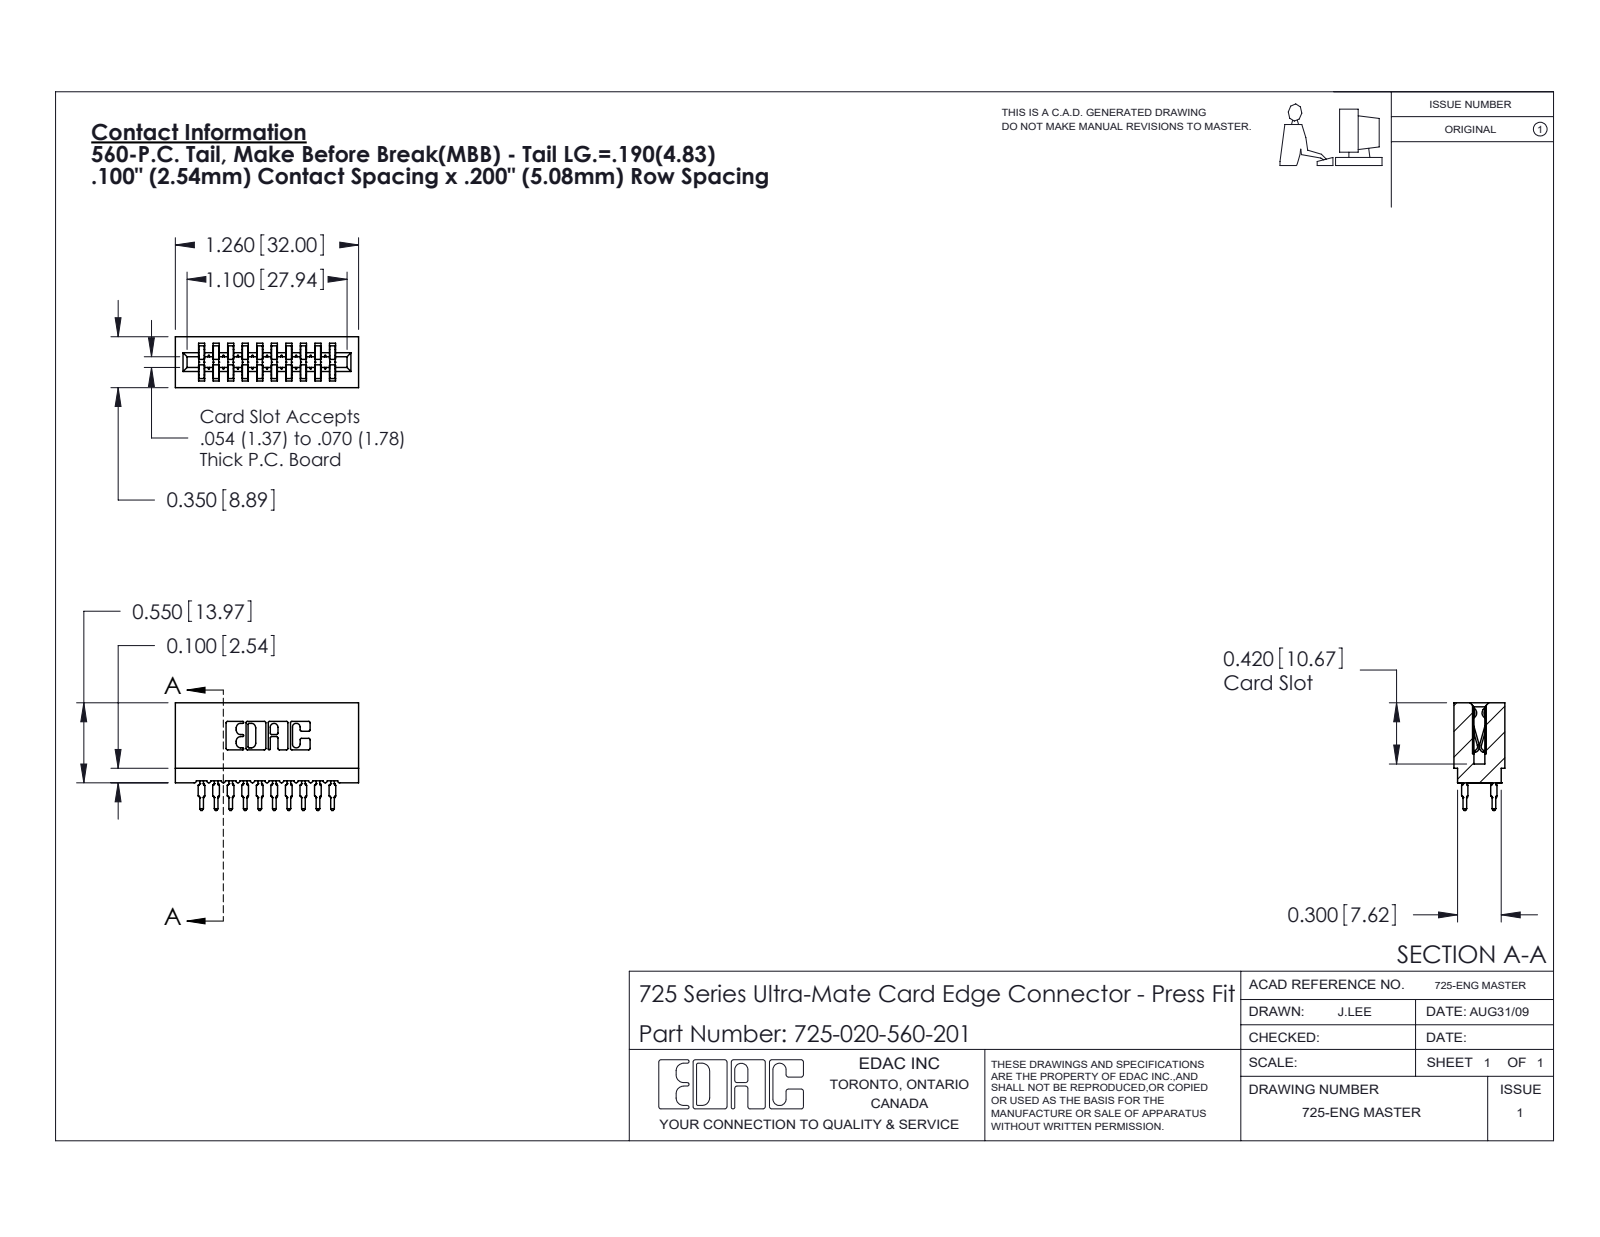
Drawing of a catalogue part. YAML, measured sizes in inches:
part_name: "725 Part_Insulator Option - 01; 745-292-001_560; 725-020-560-201"
step_written_by: "SolidWorks 2020 (CONFIG_CONTROL_DESIGN)"
units: inches
bodies: {solids: 21, faces: 2065, planar: 1075, cylindrical: 470, other: 520}
overall_size: [1.26, 0.741, 0.35]
volume: 0.169
surface_area: 8.507
partial_cylinders:
  - {radius: 0.021, count: 40}
  - {radius: 0.01, count: 22}
  - {radius: 0.015, count: 20}
  - {radius: 0.005, count: 8}
  - {radius: 0.011, count: 8}
  - {radius: 0.007, count: 6}
  - {radius: 0.031, count: 6}
  - {radius: 0.026, count: 3}
face_to_face_distances: [0.2, 0.1, 0.3, 0.4, 0.042, 0.5, 0.142, 0.058, 0.242, 0.158]
